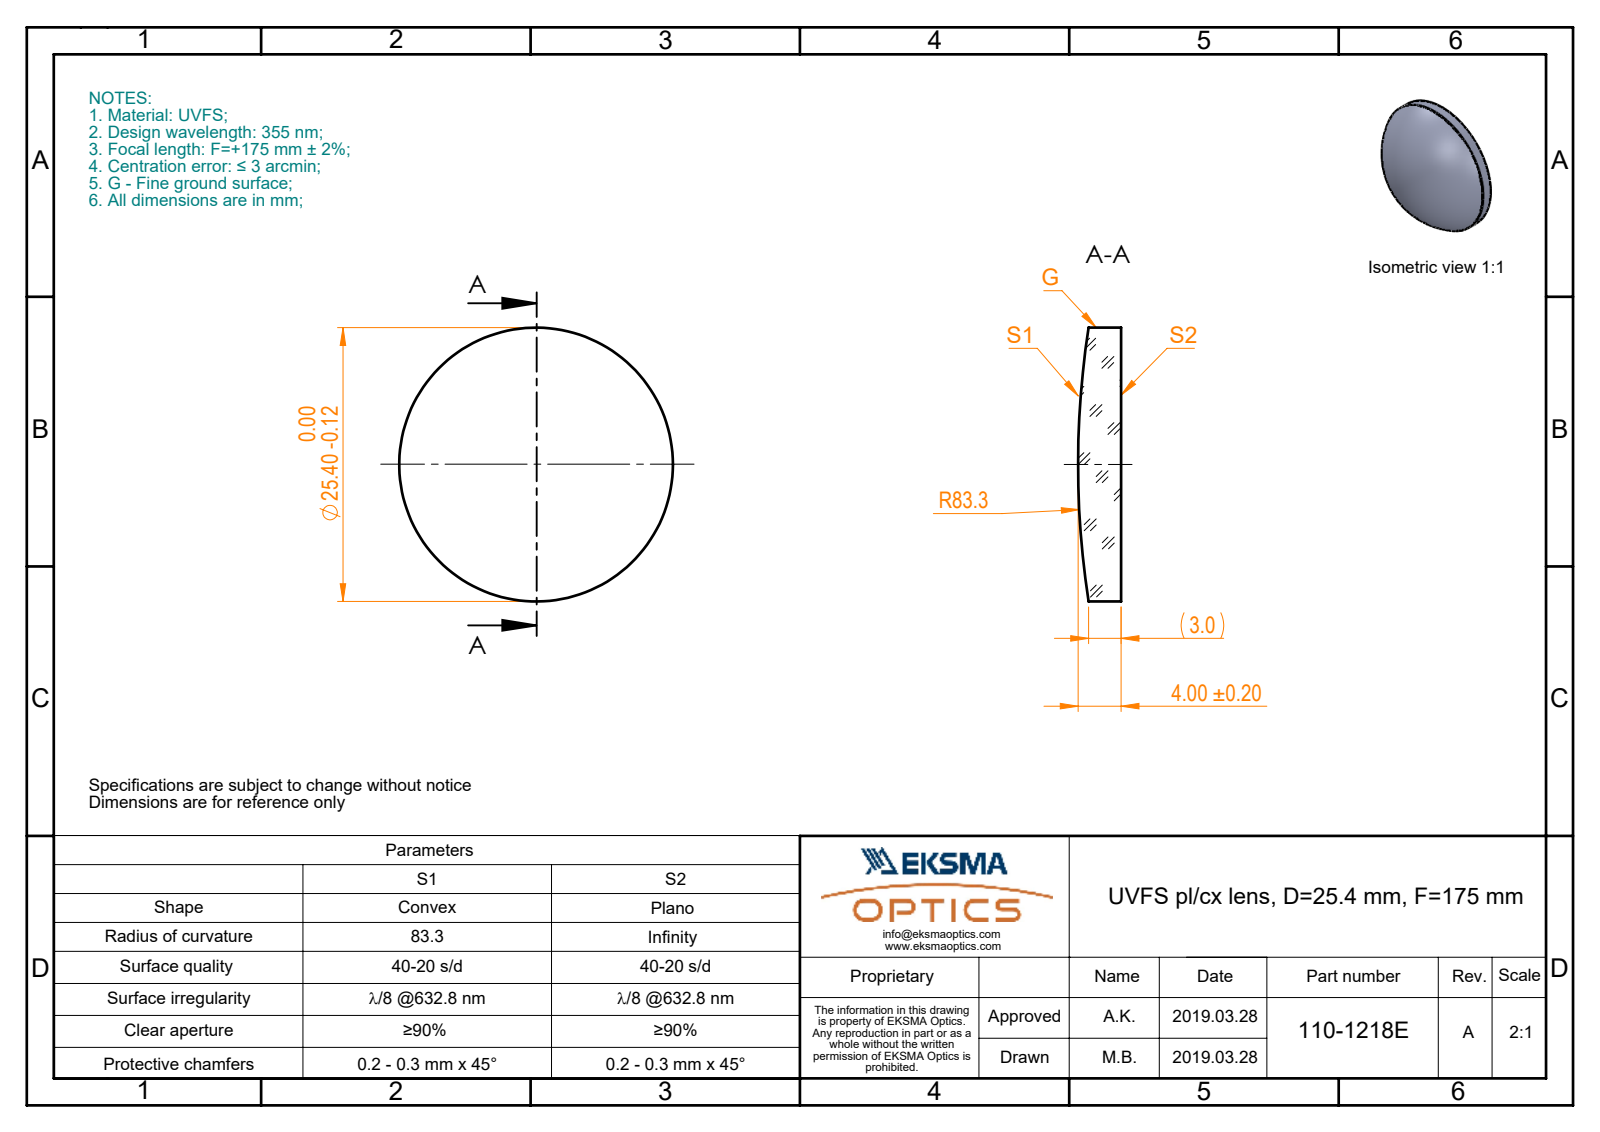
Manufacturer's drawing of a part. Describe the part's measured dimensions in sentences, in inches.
The part is named "110-1218E UVFS pl-cx 25.4 F175". Its 3-D file was written by "SolidWorks 2017 (CONFIG_CONTROL_DESIGN)". It is 1 solid with 5 faces: 1 planar, 2 cylindrical and 2 other. Overall it measures 1 by 1 by 0.157 inches. Its volume is 0.109 cubic inches and its surface area 1.95 square inches. Round bosses or shafts: 1 of diameter 1.
